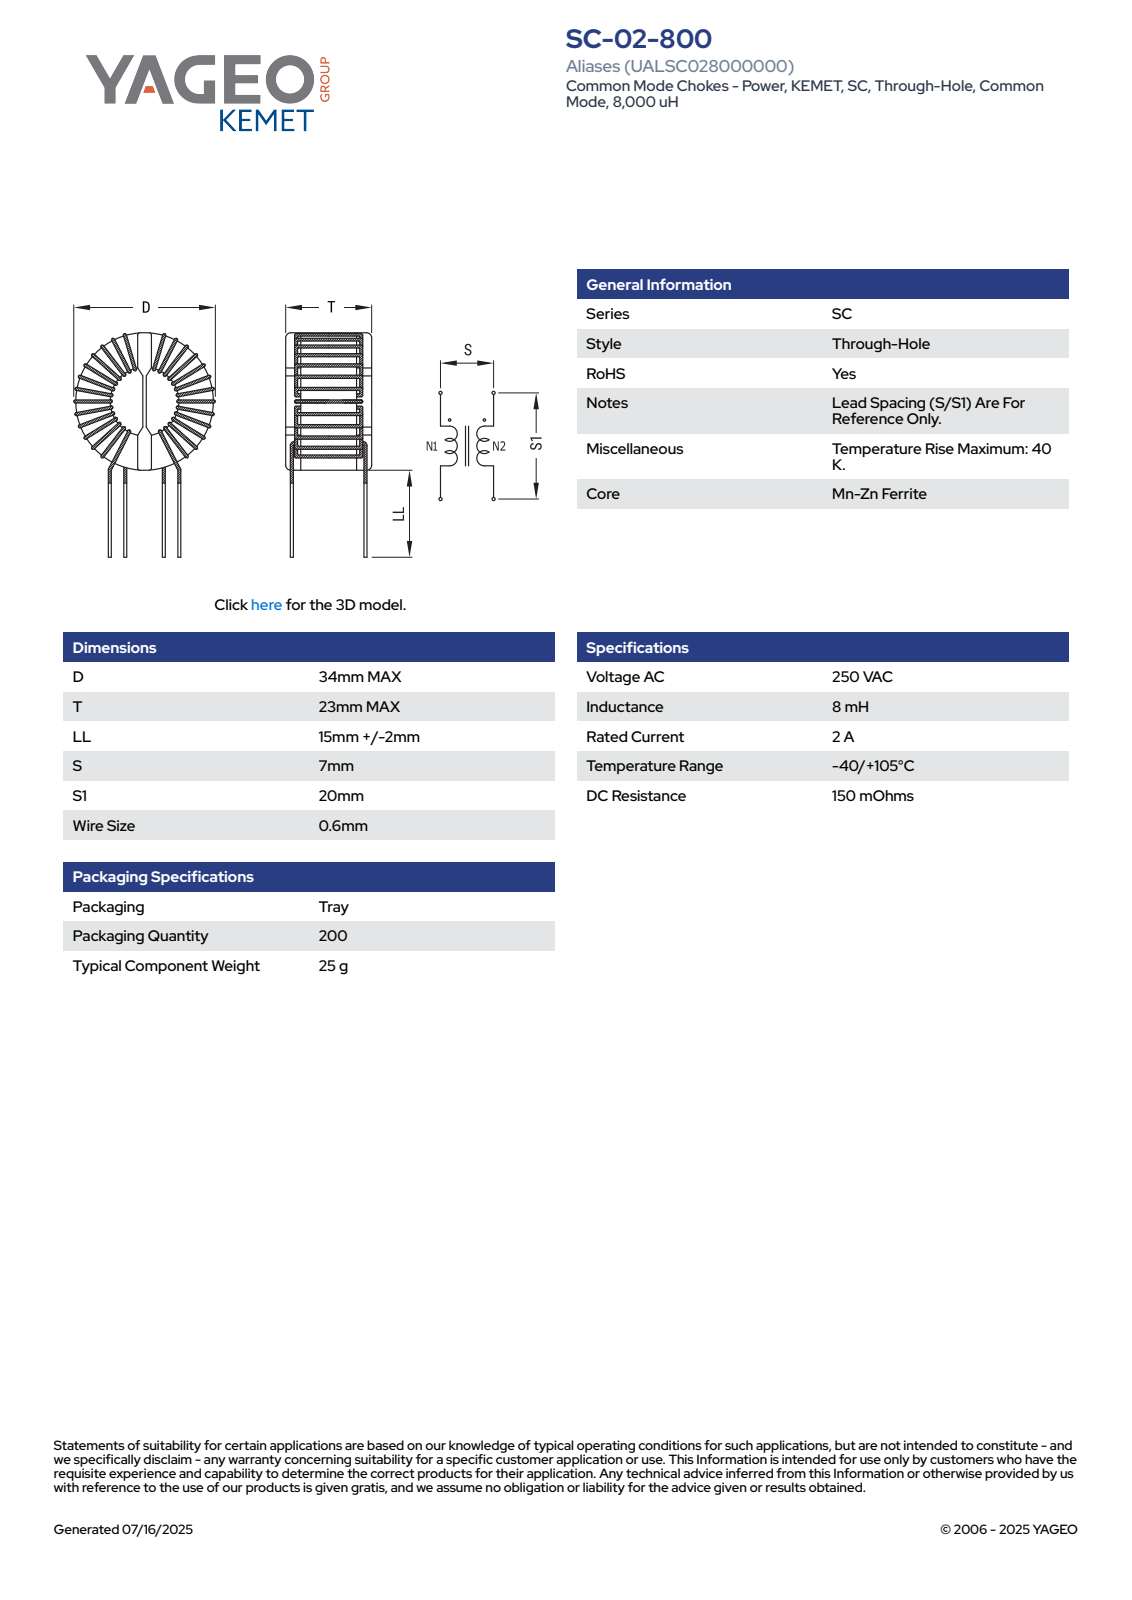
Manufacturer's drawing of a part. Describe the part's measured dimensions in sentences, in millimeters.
The part is named "SC-02-800". Its 3-D file was written by "SolidWorks 2018 (AUTOMOTIVE_DESIGN)". It is 1 solid with 273 faces: 113 planar, 91 cylindrical and 69 other. Overall it measures 45.32 by 34 by 23 millimeters. Its volume is 15 058 cubic millimeters and its surface area 6 435 square millimeters. Round bosses or shafts: 8 of diameter 0.6. Partial cylindrical surfaces (rounded edges, fillets, slot ends): 16 of radius 0.3, 6 of radius 0.2, 2 of radius 0.5, 1 of radius 4.5, 1 of radius 6.65, 1 of radius 7.35, 1 of radius 7.45, 1 of radius 7.5. The main face-to-face distances are 20.2, 1.2, 2, 0.8, 3.2, 2.5, 17.7, 1.4, 21.6, 19.1.
